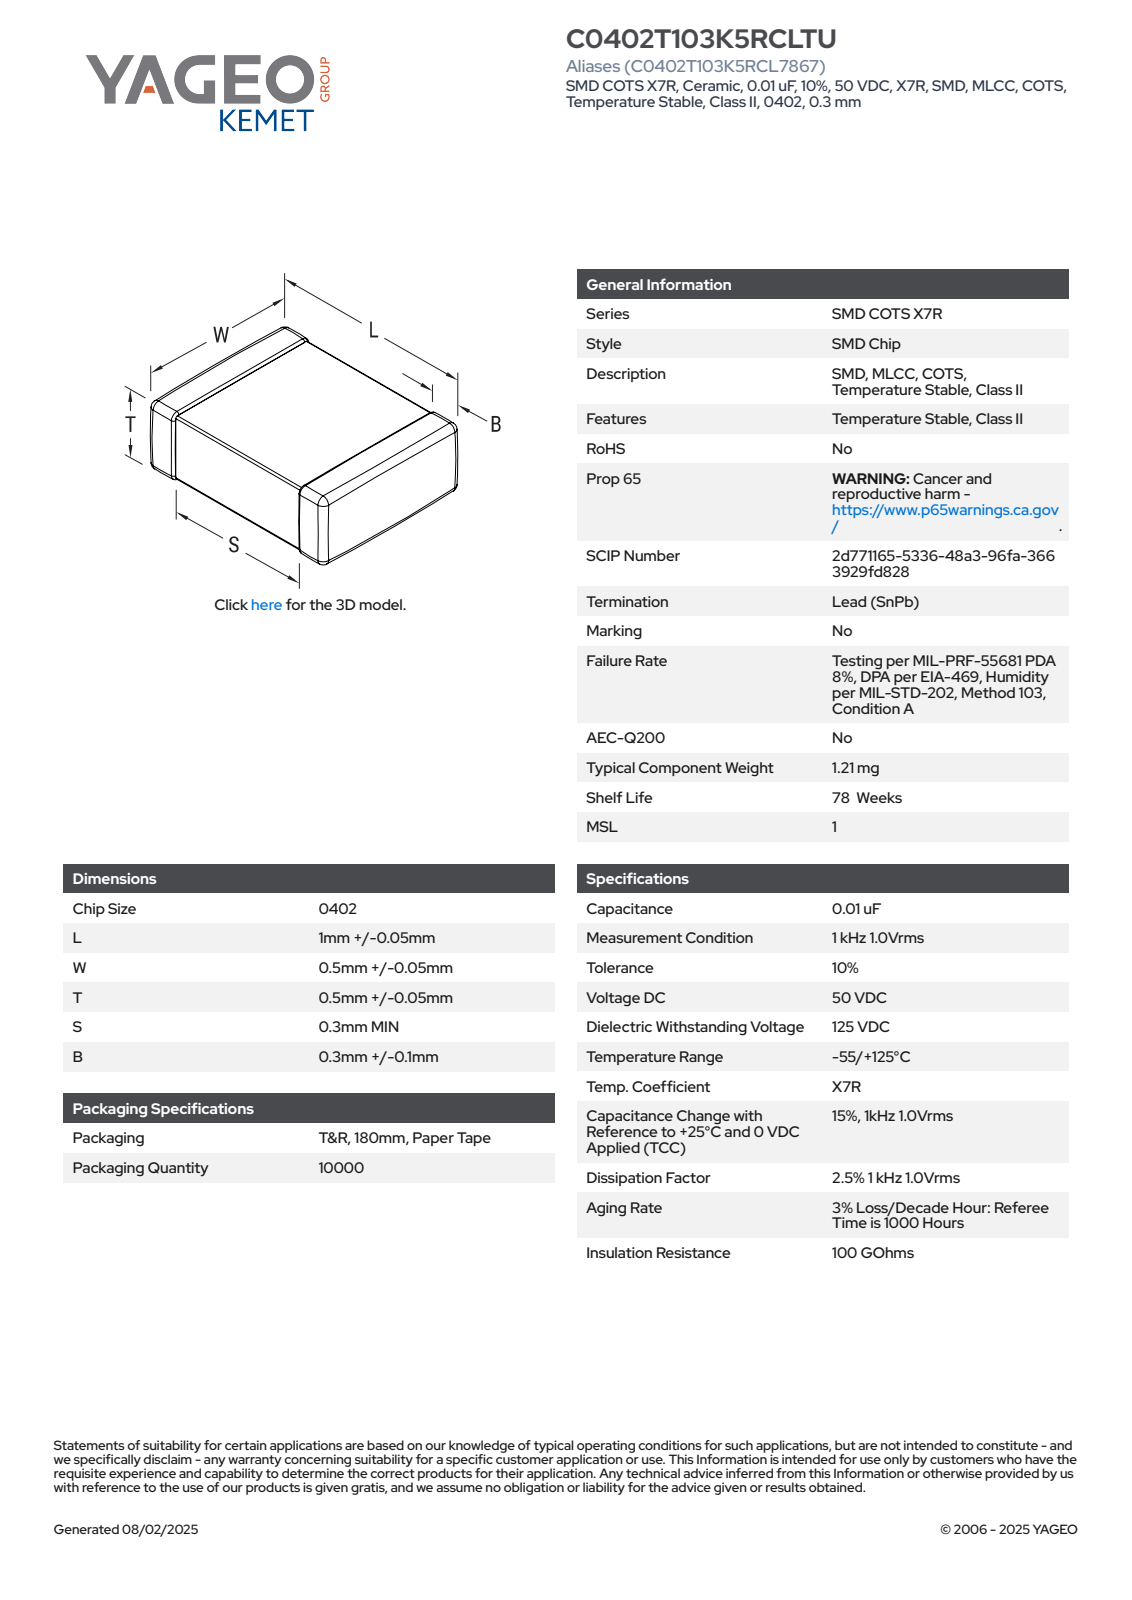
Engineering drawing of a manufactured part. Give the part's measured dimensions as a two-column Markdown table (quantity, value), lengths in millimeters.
| quantity | value |
| --- | --- |
| part name | CCSM_STD_0402_L1.05W0.55T0.55S0.5B0.4 |
| STEP written by | SolidWorks 2021 (AUTOMOTIVE_DESIGN) |
| units | millimeters |
| bodies | 4 solids, 129 faces (71 planar, 42 cylindrical, 16 other) |
| overall size | 1.05 × 0.55 × 0.55 |
| volume | 0.311 mm³ |
| surface area | 3 mm² |
| main face-to-face distances | 0.55, 0.54, 1.05, 0.53, 0.49, 0.56, 0.57, 0.48, 0.5, 0.52 |
